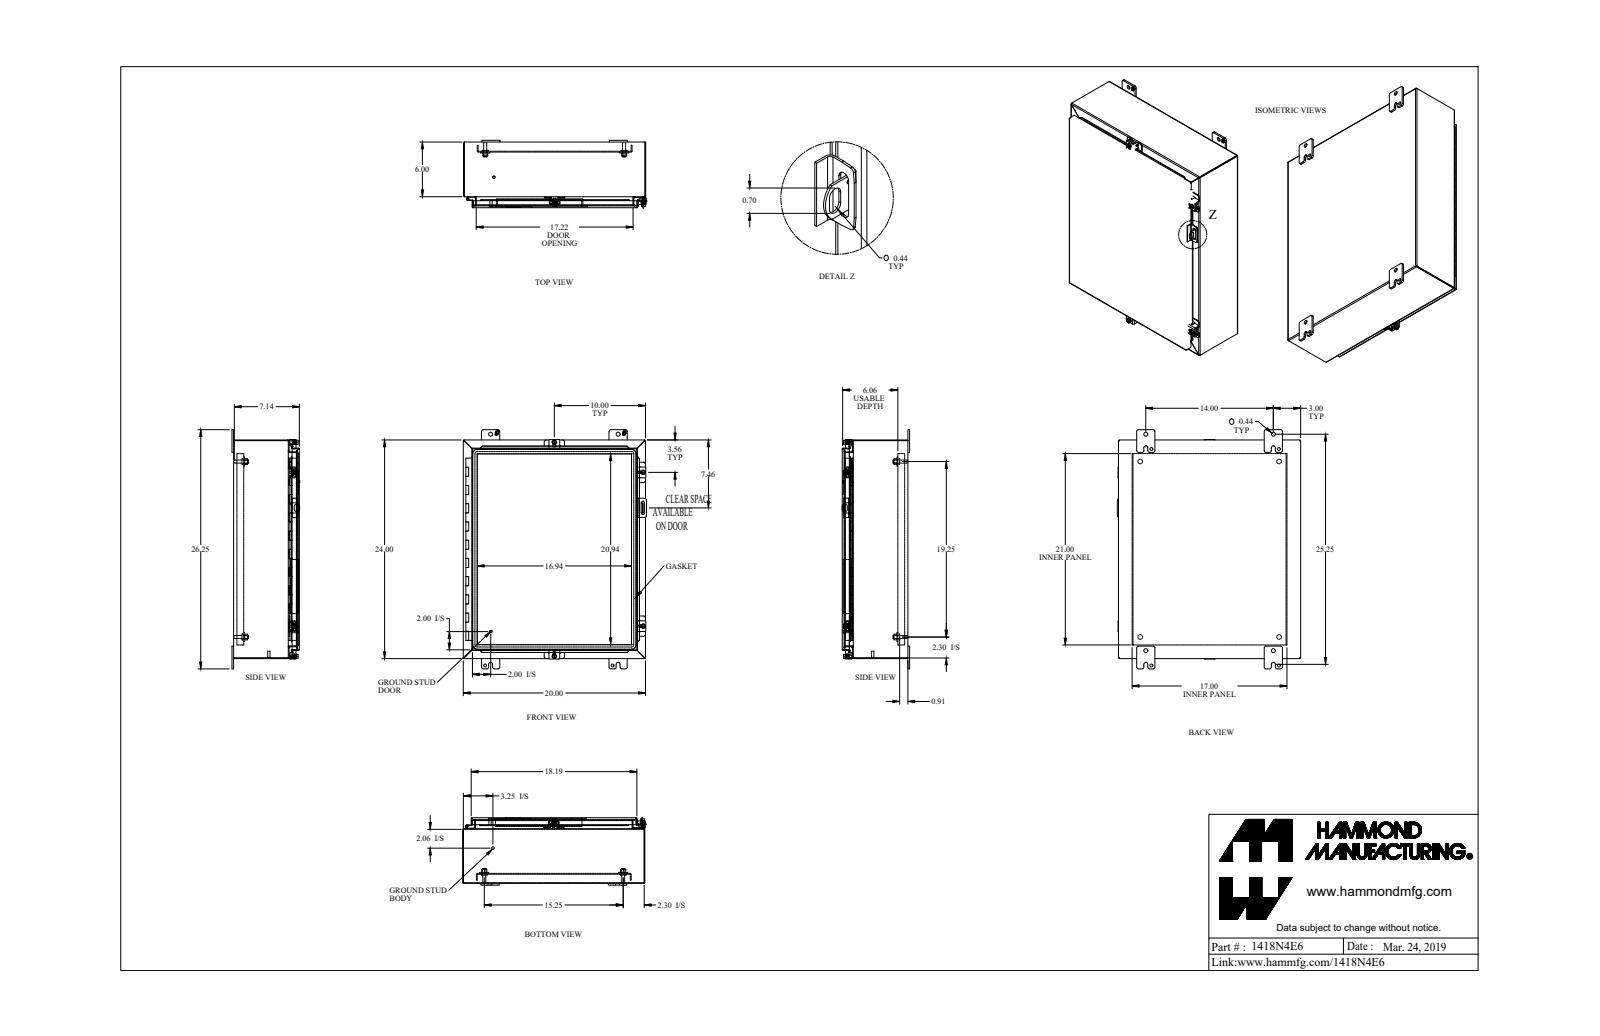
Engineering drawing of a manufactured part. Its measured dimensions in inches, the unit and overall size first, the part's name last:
Units: inches
Overall size (bounding box): 26.25 × 20.126 × 7.437
Round holes (diameter × count): ⌀0.213 ×4, ⌀0.313 ×4, ⌀0.375 ×4, ⌀0.437 ×4, ⌀0.5 ×4, ⌀0.265 ×2, ⌀0.265 ×2, ⌀0.307 ×2, ⌀0.445 ×2, ⌀0.125 ×1, ⌀0.187 ×1
Round bosses / shafts (diameter × count): ⌀0.65 ×4, ⌀0.5 ×4, ⌀0.39 ×4, ⌀0.375 ×4, ⌀0.33 ×4, ⌀0.244 ×4, ⌀1 ×2, ⌀0.281 ×2
Partial cylindrical surfaces — rounded edges, fillets, slot ends (radius × count): R0.188 ×26, R0.036 ×24, R0.108 ×24, R0.048 ×21, R0.143 ×21, R0.25 ×20, R0.125 ×10, R0.045 ×8
Main face-to-face distances: 0.072, 0.072, 7.066, 7.138, 7.138, 7.21, 0.095, 6.106, 6.034, 1.032
Hole centre spacings: 24.559, 7.916, 14, 19.25, 22.694, 2.434, 7.915, 14.702
Volume: 173.3 in³ · Surface area: 4 523 in²
Bodies: 39 solids, 1412 faces (853 planar, 474 cylindrical, 85 other)
Part name (STEP PRODUCT): 1418N4E6_Default
STEP written by: SolidWorks 2019 (CONFIG_CONTROL_DESIGN)
